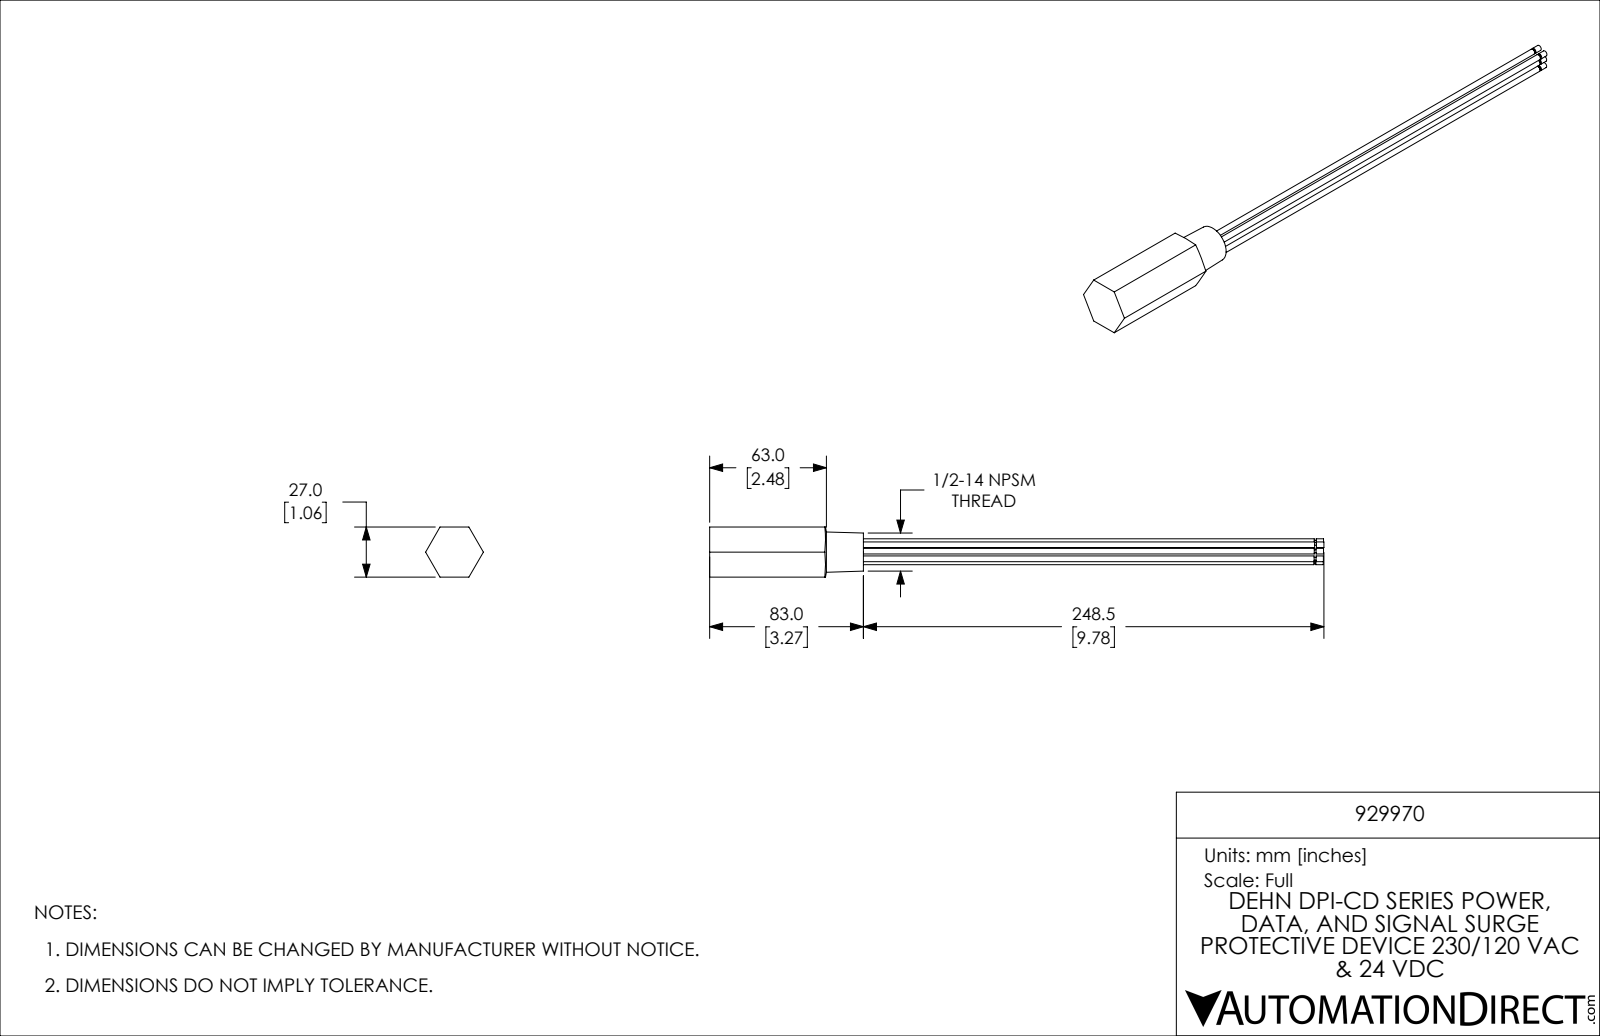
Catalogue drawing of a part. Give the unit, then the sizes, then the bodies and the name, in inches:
Units: inches
Overall size (bounding box): 13.052 × 1.227 × 1.063
Round holes (diameter × count): ⌀0.614 ×1
Round bosses / shafts (diameter × count): ⌀0.122 ×5, ⌀0.057 ×5
Main face-to-face distances: 1.063, 2.835, 0.433, 3.268, 0.157, 0.197, 0.039, 0.014, 0.159, 0.198
Volume: 3.317 in³ · Surface area: 33.4 in²
Bodies: 1 solid, 61 faces (24 planar, 33 cylindrical, 4 other)
Part name (STEP PRODUCT): 929970
STEP written by: SolidWorks 2019 (CONFIG_CONTROL_DESIGN)
